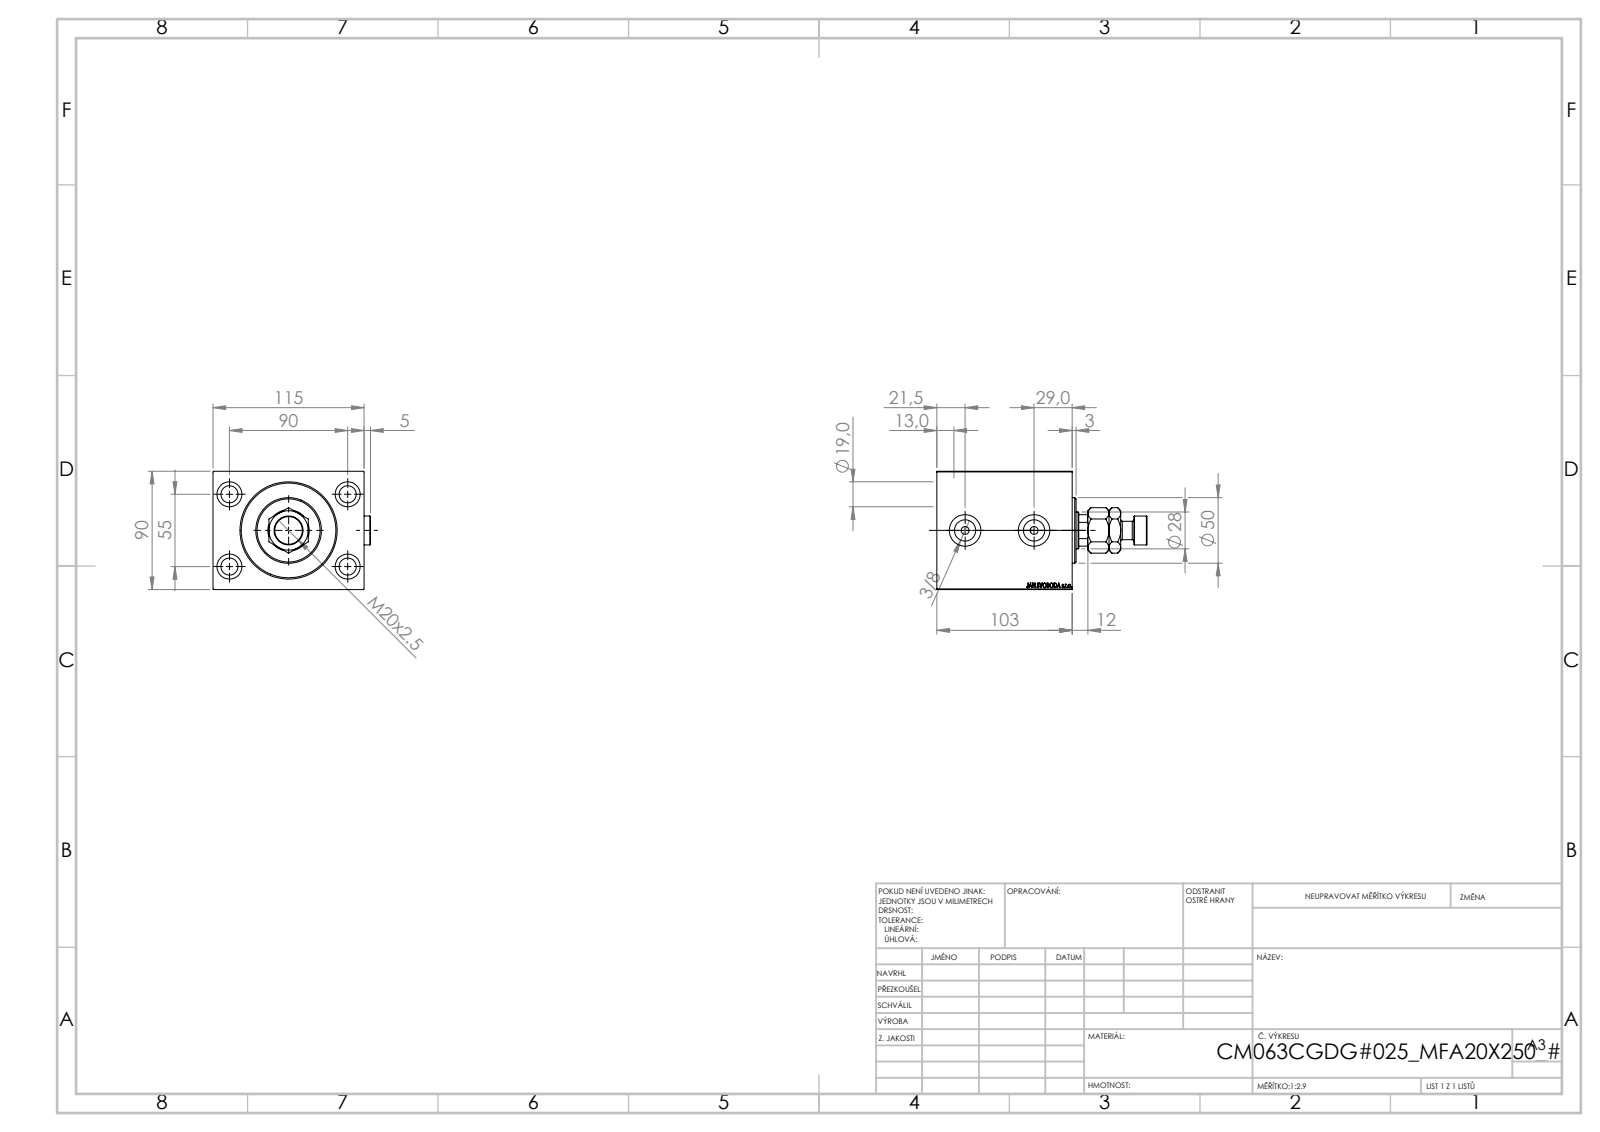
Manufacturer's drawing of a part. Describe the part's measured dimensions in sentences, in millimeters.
The part is named "V450CM_VC_B; V450CM_C_VCP; MFA; V450CM_C_Body (+1 more)". Its 3-D file was written by "SolidWorks 2019 (CONFIG_CONTROL_DESIGN)". It is 6 solids with 969 faces: 459 planar, 80 cylindrical and 430 other. Overall it measures 160 by 119.9 by 90 millimeters. Its volume is 987 712 cubic millimeters and its surface area 132 780 square millimeters. Round holes: 4 of diameter 13, 4 of diameter 19, 2 of diameter 6, 2 of diameter 16.17, 2 of diameter 24, 1 of diameter 18.5, 1 of diameter 28, 1 of diameter 31.5, 1 of diameter 63, 1 of diameter 65, 1 of diameter 72. Round bosses or shafts: 3 of diameter 22, 1 of diameter 50, 1 of diameter 14. Partial cylindrical surfaces (rounded edges, fillets, slot ends): 1 of radius 13.5. The main face-to-face distances are 90, 115, 103, 52, 51, 21.6, 29.4, 81.4, 10, 71.4. The hole center spacings are 52.74, 55, 90, 105.48, 52.5.
